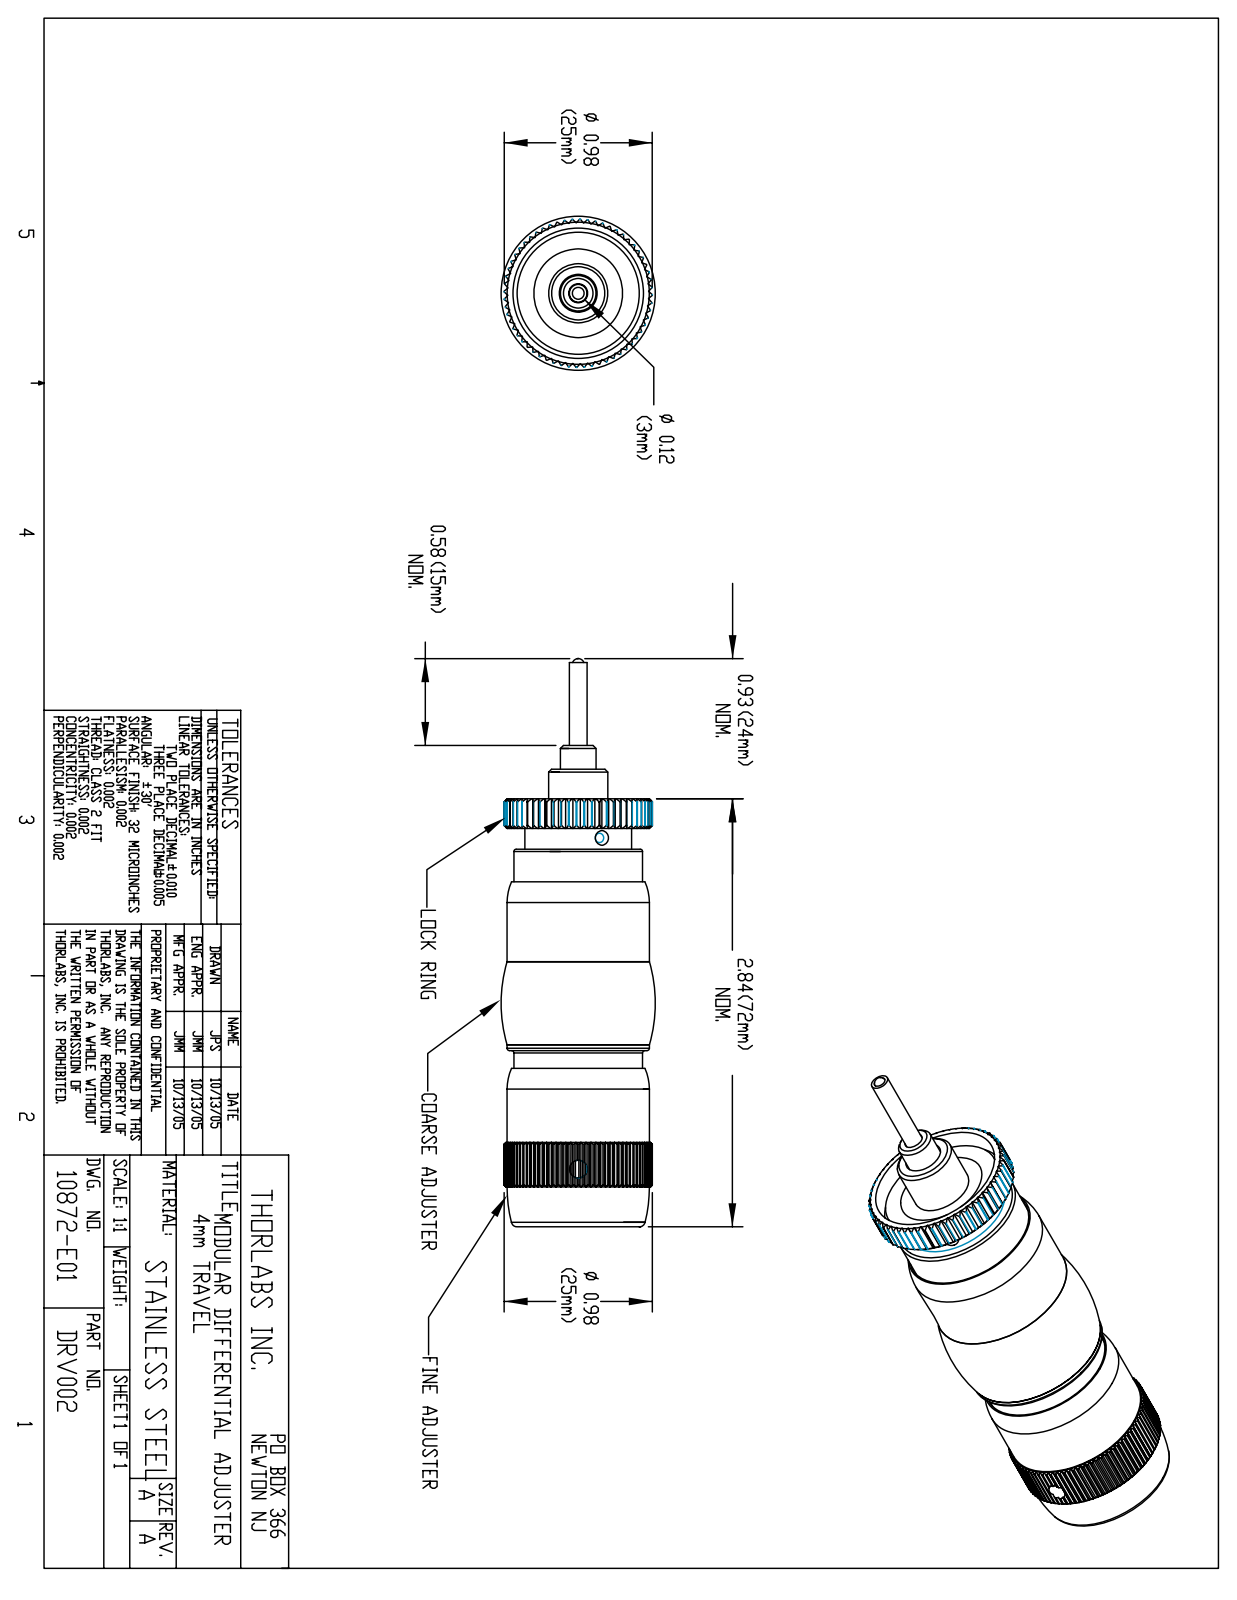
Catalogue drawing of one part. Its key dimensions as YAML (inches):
part_name: "10872-E0W"
step_written_by: "SolidWorks 2007 (AUTOMOTIVE_DESIGN)"
units: inches
bodies: {solids: 0, faces: 869, planar: 350, cylindrical: 185, other: 334}
overall_size: [3.776, 1.024, 1.024]
round_holes:
  - {diameter: 0.098, count: 1}
  - {diameter: 0.118, count: 1}
  - {diameter: 0.126, count: 1}
  - {diameter: 0.252, count: 1}
  - {diameter: 0.866, count: 1}
round_bosses_or_shafts:
  - {diameter: 0.945, count: 1}
  - {diameter: 0.854, count: 1}
  - {diameter: 0.709, count: 1}
  - {diameter: 0.394, count: 1}
  - {diameter: 0.236, count: 1}
  - {diameter: 0.118, count: 1}
partial_cylinders:
  - {radius: 0.492, count: 1}
face_to_face_distances: [0.098, 0.051, 0.661, 0.047, 0.138, 0.189, 0.236, 0.197, 0.661, 0.679]
